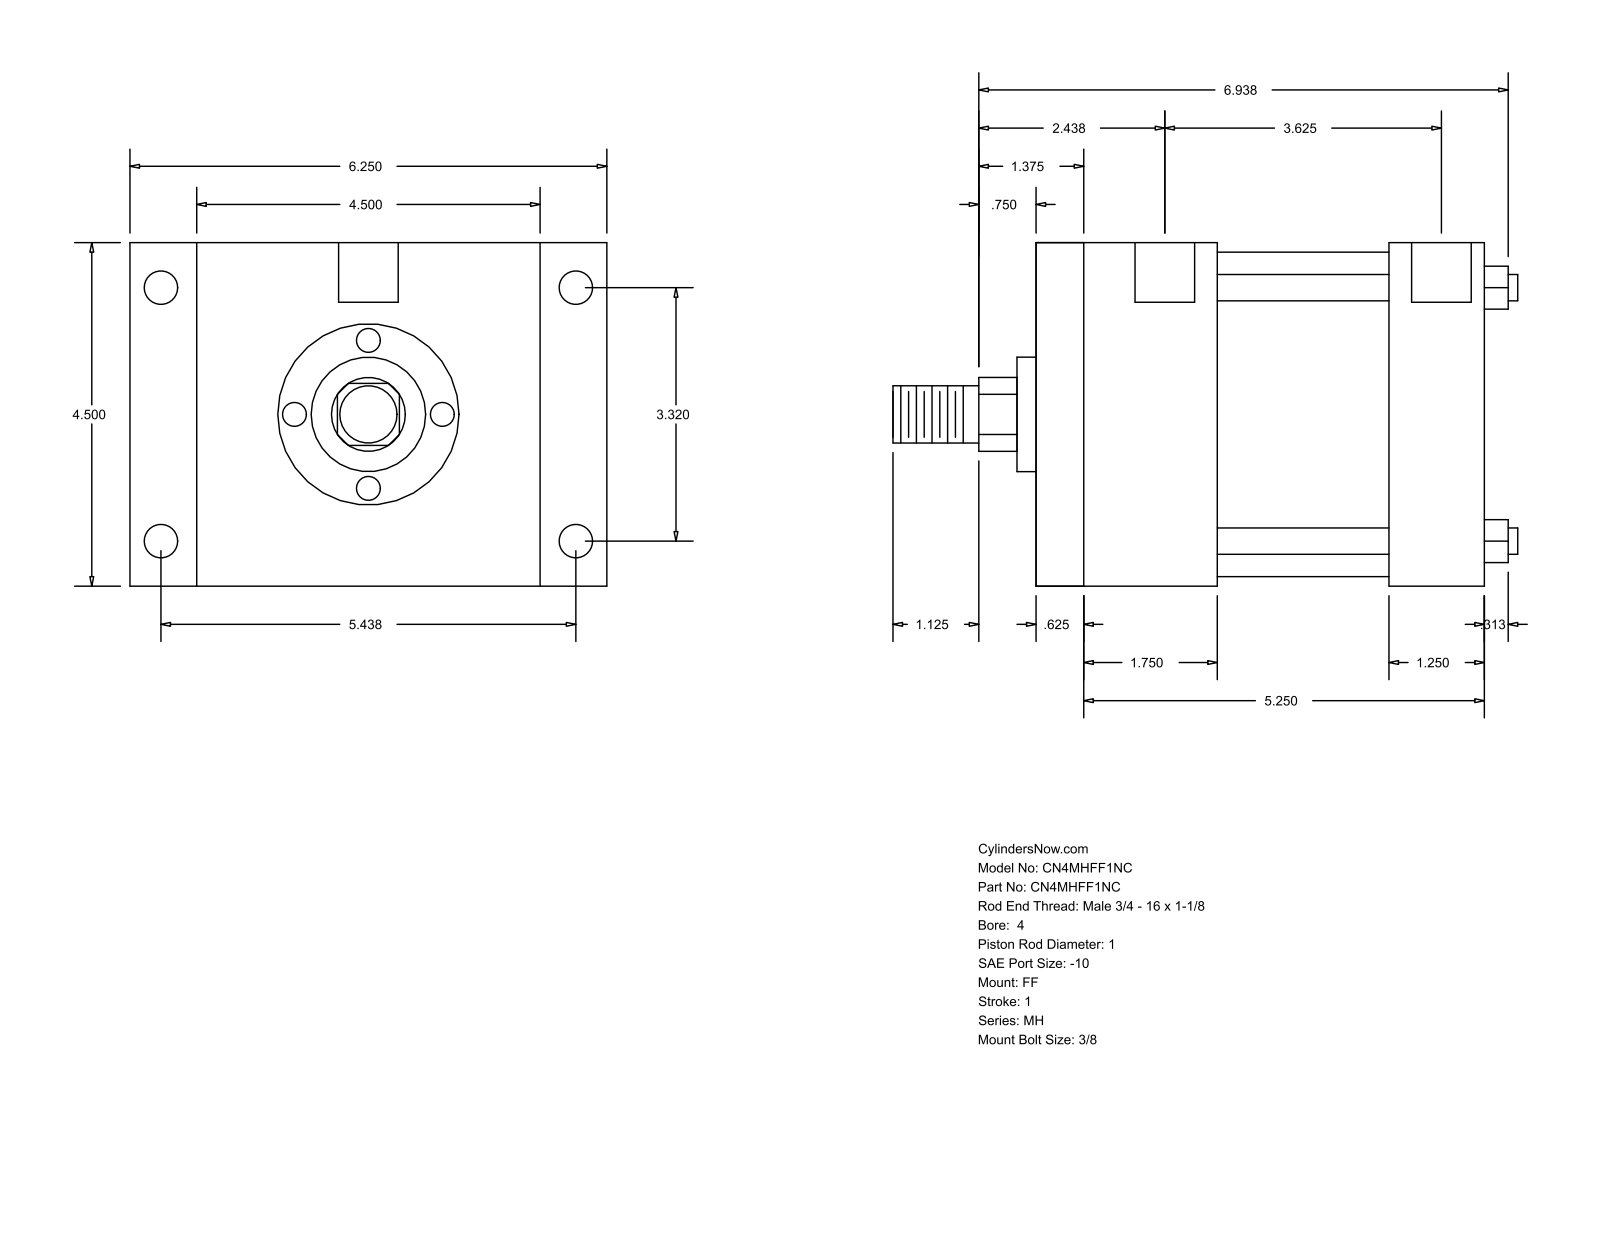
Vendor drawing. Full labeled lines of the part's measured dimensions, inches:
Part name (STEP PRODUCT): MH_FF__0400_1
STEP written by: GSSL Pune (CONFIG_CONTROL_DESIGN)
Units: inches
Bodies: 0 solids, 92 faces (64 planar, 28 cylindrical, 0 other)
Overall size (bounding box): 8.187 × 6.25 × 4.5
Round holes (diameter × count): ⌀0.344 ×4, ⌀0.438 ×4, ⌀0.781 ×2
Round bosses / shafts (diameter × count): ⌀0.345 ×4, ⌀4.25 ×1, ⌀1.5 ×1, ⌀1 ×1, ⌀0.75 ×1
Partial cylindrical surfaces — rounded edges, fillets, slot ends (radius × count): R0.484 ×1
Main face-to-face distances: 4.5, 5.875, 0.625, 5.25, 5.375, 2.375, 1.75, 3.5, 4.625, 4
Hole centre spacings: 0.062, 3.32, 3.687, 3.75, 5.438, 6.371, 3.625
